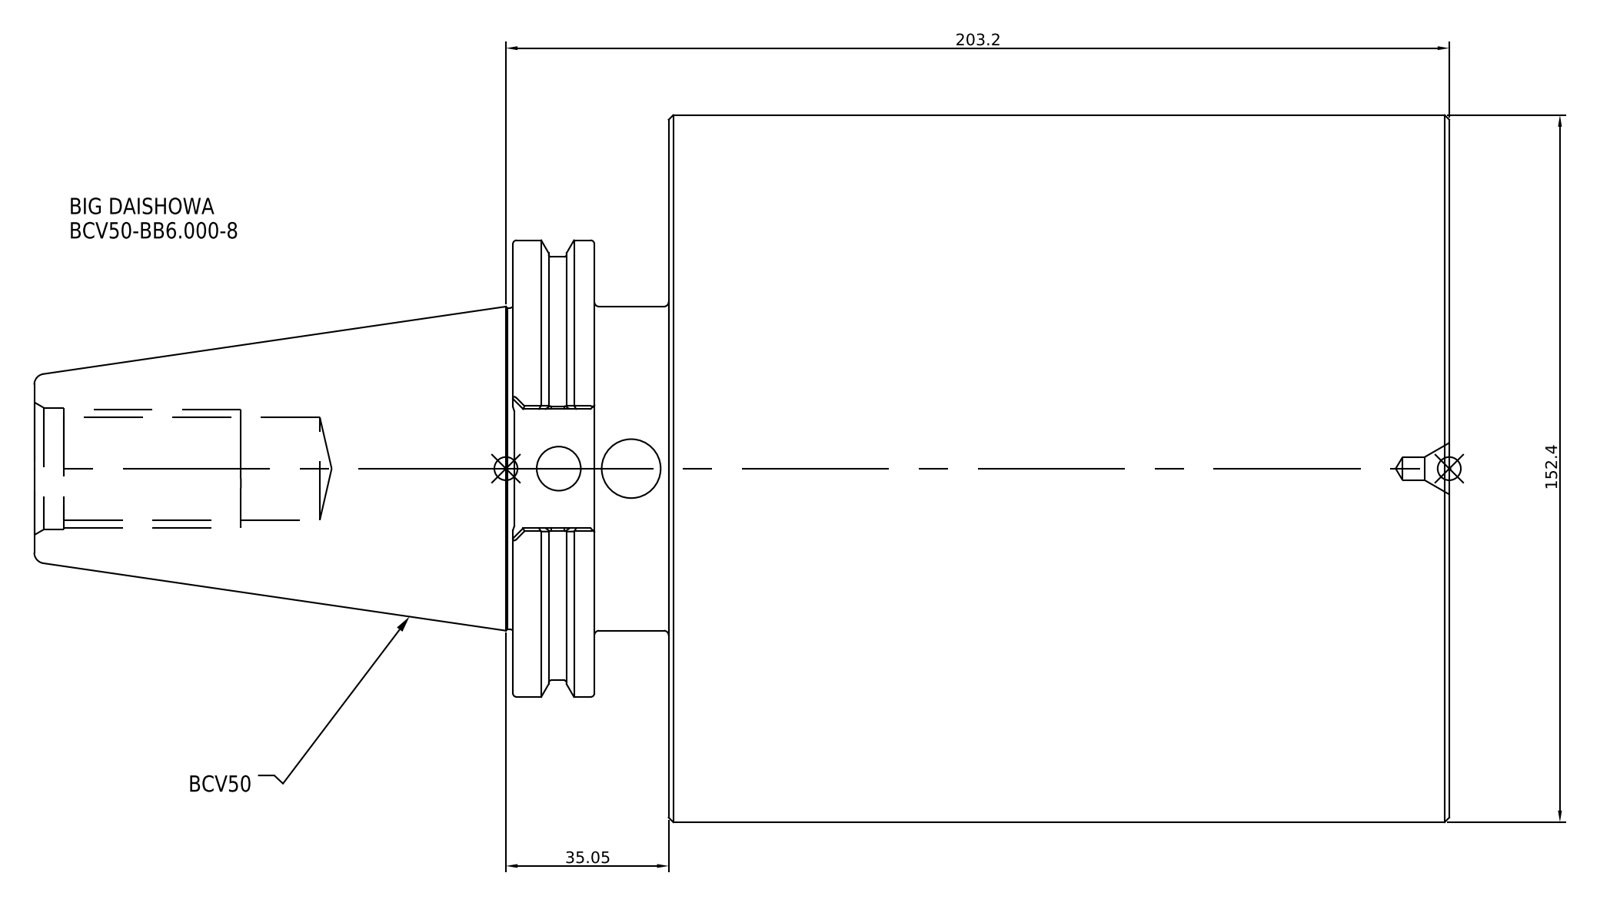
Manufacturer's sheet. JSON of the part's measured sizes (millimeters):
{"part_name": "BVC50_BB6_000_8", "step_written_by": "SolidWorks 2021 (CONFIG_CONTROL_DESIGN)", "units": "millimeters", "bodies": {"solids": 1, "faces": 16, "planar": 7, "cylindrical": 6, "other": 3}, "overall_size": [304.8, 152.4, 152.4], "volume_mm3": 3511000, "surface_area_mm2": 150323, "round_bosses_or_shafts": [[152.4, 1], [98.43, 1], [91.29, 1], [69.85, 1]], "face_to_face_distances": [168.2, 201.7, 33.5, 184.15, 15.95, 17.55, 304.8, 136.6, 120.65, 103.1]}
